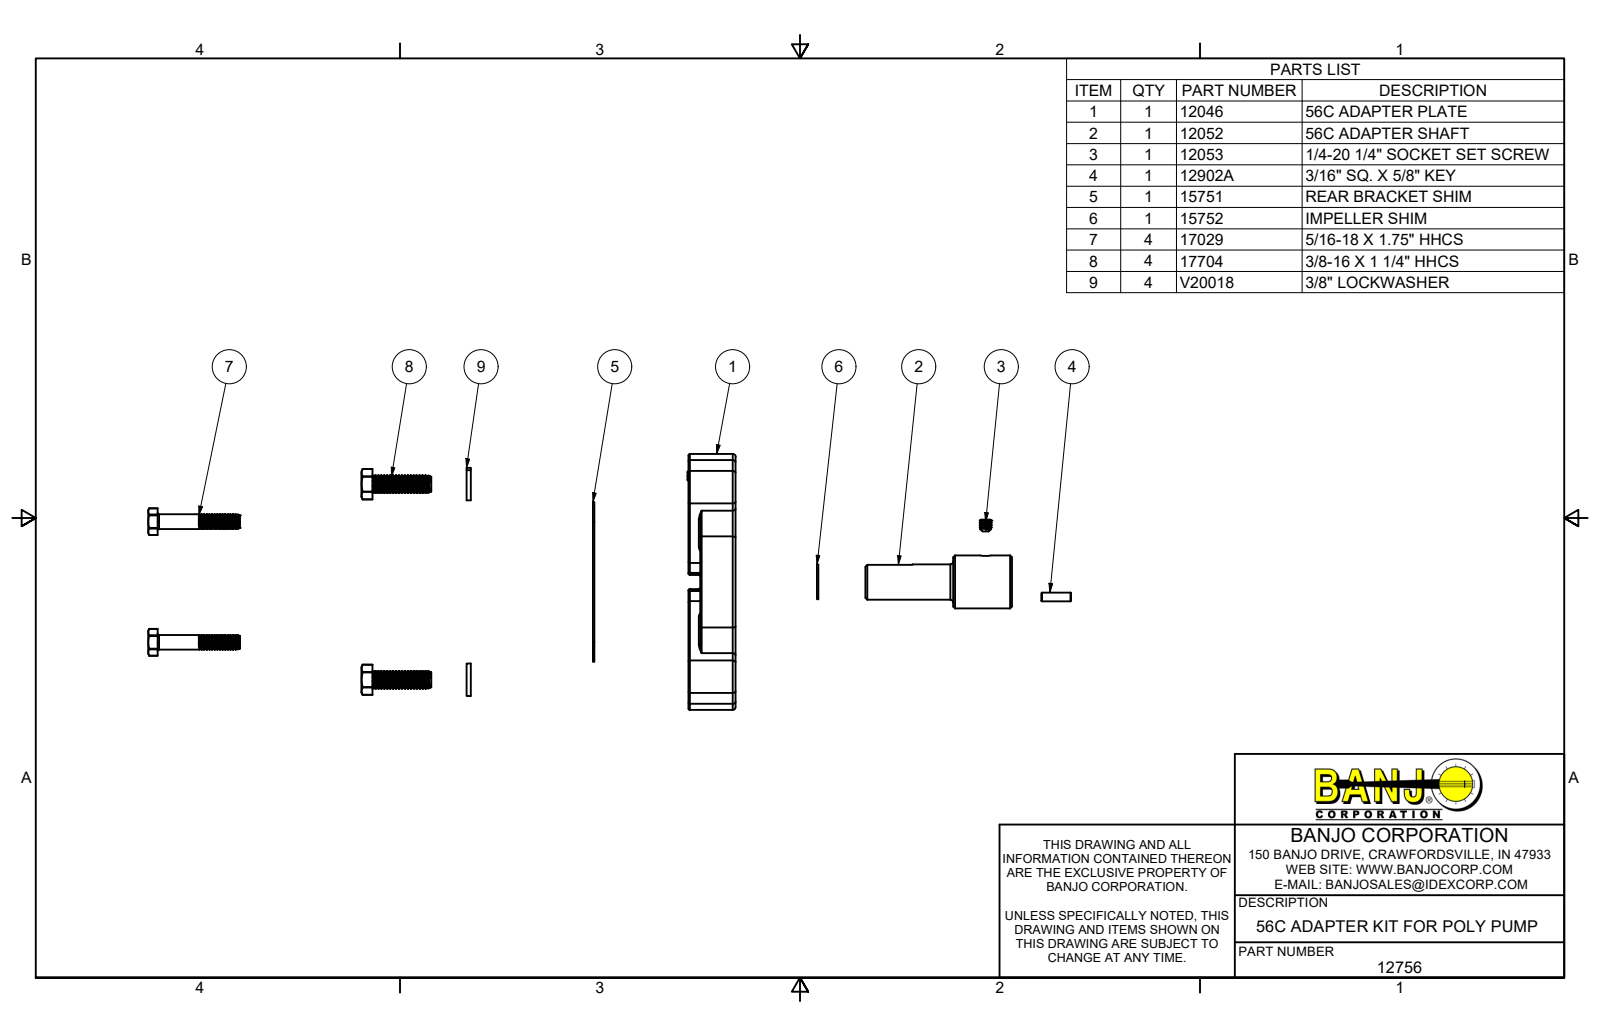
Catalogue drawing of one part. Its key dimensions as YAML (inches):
part_name: "12756; 12046; 12046X; I516018072 (+8 more)"
step_written_by: "Autodesk Inventor 2019 (AUTOMOTIVE_DESIGN)"
units: inches
bodies: {solids: 22, faces: 3525, planar: 889, cylindrical: 1116, other: 1520}
overall_size: [5.436, 5.436, 3.802]
volume: 19.05
surface_area: 155.7
round_holes:
  - {diameter: 0.5, count: 5}
  - {diameter: 0.252, count: 4}
  - {diameter: 0.323, count: 4}
  - {diameter: 0.359, count: 4}
  - {diameter: 0.385, count: 4}
  - {diameter: 0.401, count: 4}
  - {diameter: 0.406, count: 4}
  - {diameter: 0.875, count: 4}
  - {diameter: 0.196, count: 2}
  - {diameter: 0.267, count: 1}
  - {diameter: 0.627, count: 1}
  - {diameter: 1.38, count: 1}
round_bosses_or_shafts:
  - {diameter: 0.324, count: 76}
  - {diameter: 0.268, count: 60}
  - {diameter: 0.687, count: 4}
  - {diameter: 0.469, count: 4}
  - {diameter: 0.439, count: 4}
  - {diameter: 0.38, count: 4}
  - {diameter: 0.375, count: 4}
  - {diameter: 0.37, count: 4}
partial_cylinders:
  - {radius: 0.03, count: 38}
  - {radius: 0.25, count: 16}
  - {radius: 0.5, count: 16}
  - {radius: 0.134, count: 8}
  - {radius: 0.162, count: 8}
  - {radius: 0.06, count: 4}
  - {radius: 0.284, count: 4}
  - {radius: 0.322, count: 4}
face_to_face_distances: [0.031, 0.875, 0.906, 0.125, 1, 1.031, 0.281, 0.625, 0.5, 0.75]
hole_center_spacings: [3.452, 1.125, 1.812, 2.563, 2.937, 4.154, 4.75, 3.625]
